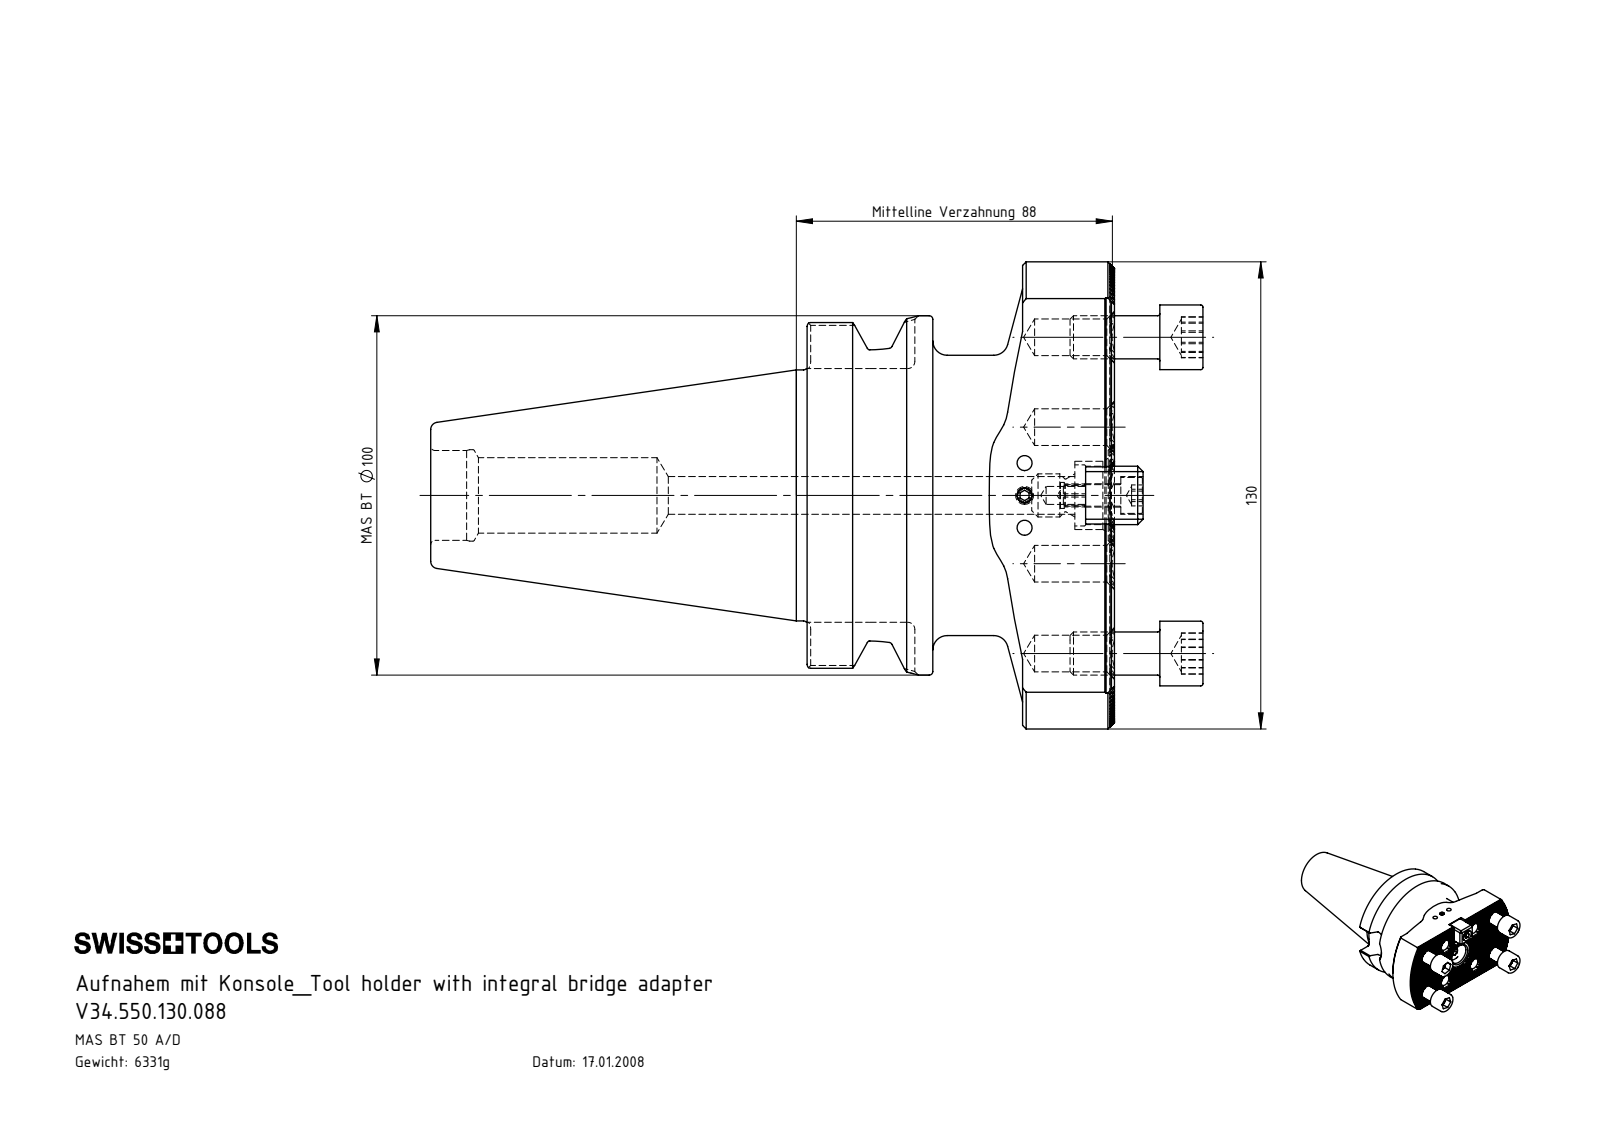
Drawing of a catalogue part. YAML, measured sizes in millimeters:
part_name: "DIN 908 - M12x1.5; ISO 4762 - M12 x 25; Ko1-ER1.001.016_A; ISO 4026 - M5 x 8 (+3 more)"
step_written_by: "SolidWorks 2017 (AUTOMOTIVE_DESIGN)"
units: millimeters
bodies: {solids: 10, faces: 747, planar: 488, cylindrical: 164, other: 95}
overall_size: [215.01, 130, 100]
volume: 806426
surface_area: 100043
round_holes:
  - {diameter: 10.2, count: 8}
  - {diameter: 4.2, count: 3}
  - {diameter: 10.5, count: 2}
  - {diameter: 5, count: 1}
  - {diameter: 6.5, count: 1}
  - {diameter: 7.24, count: 1}
  - {diameter: 19, count: 1}
  - {diameter: 21, count: 1}
  - {diameter: 25, count: 1}
  - {diameter: 25.45, count: 1}
round_bosses_or_shafts:
  - {diameter: 12, count: 5}
  - {diameter: 18, count: 4}
  - {diameter: 100, count: 1}
  - {diameter: 85, count: 1}
  - {diameter: 78, count: 1}
  - {diameter: 69.85, count: 1}
  - {diameter: 17, count: 1}
  - {diameter: 10, count: 1}
partial_cylinders:
  - {radius: 0.14, count: 34}
  - {radius: 2, count: 8}
  - {radius: 4, count: 2}
  - {radius: 7.95, count: 1}
  - {radius: 12.85, count: 1}
  - {radius: 65, count: 1}
face_to_face_distances: [1.73, 17.32, 70, 8.66, 3.46, 5.2, 6.93, 15.59, 19.05, 3.47]
hole_center_spacings: [25, 27.59, 40, 47.17, 48.33, 63, 74.63, 9]
